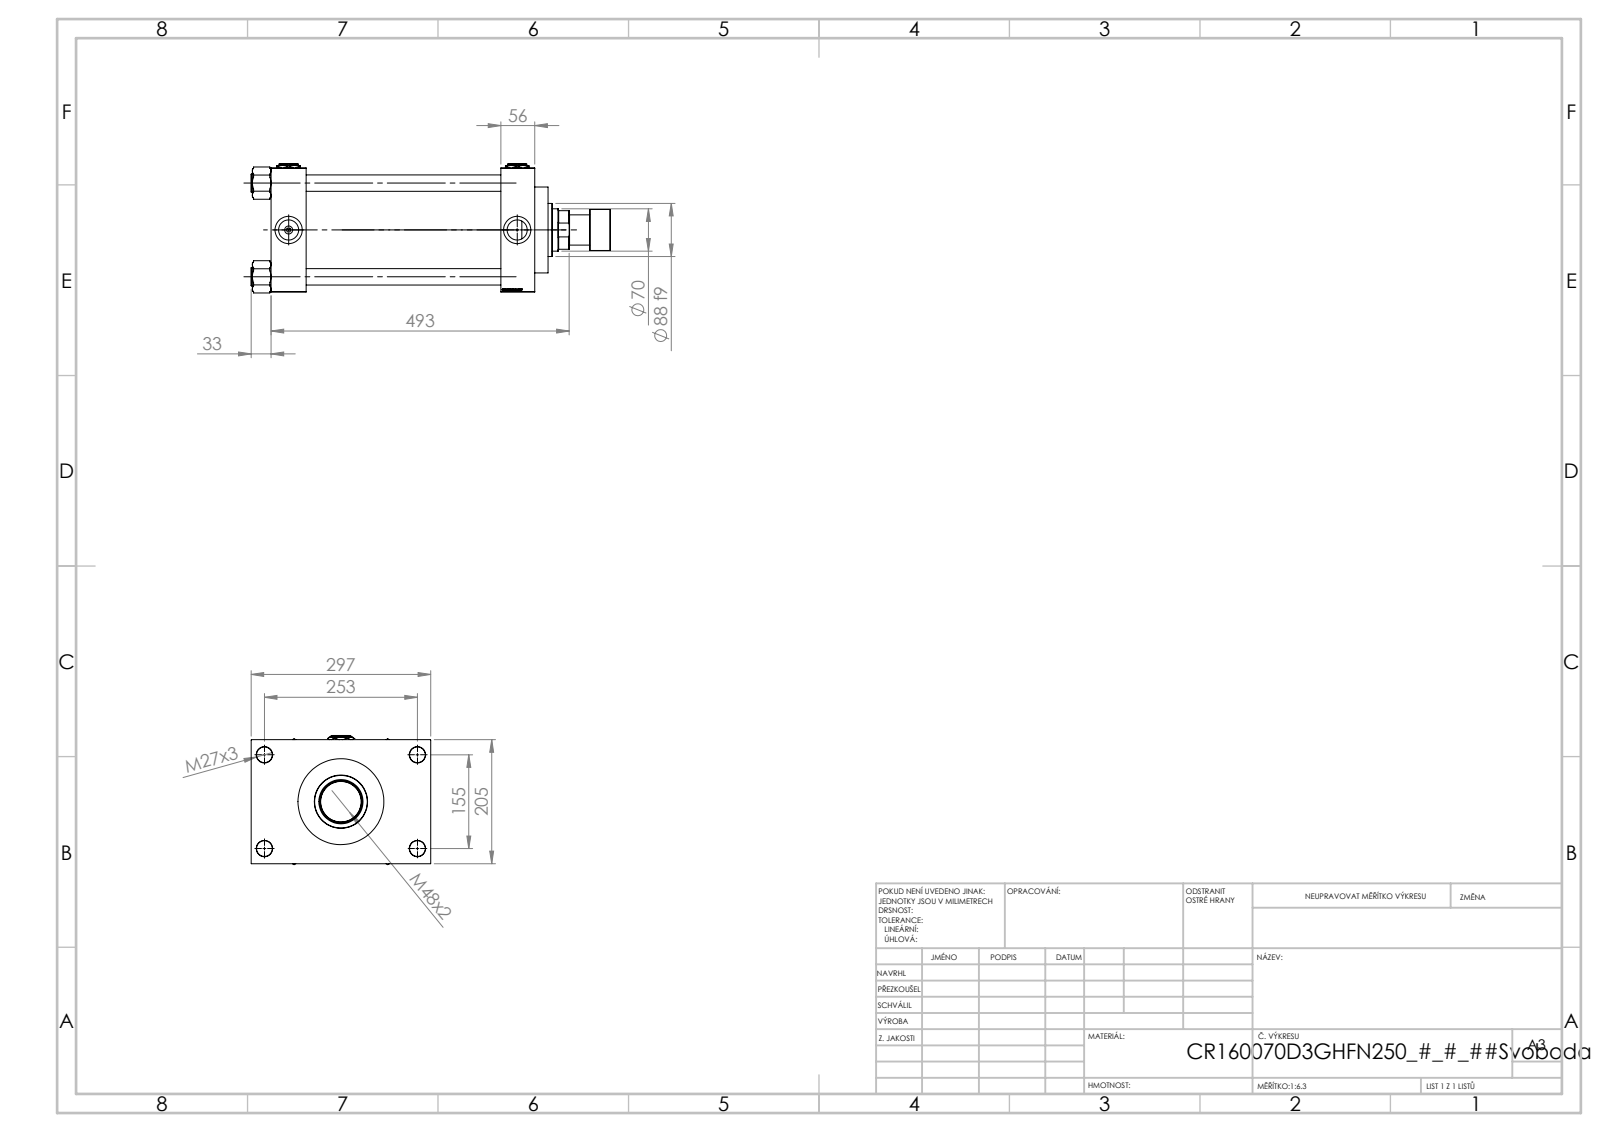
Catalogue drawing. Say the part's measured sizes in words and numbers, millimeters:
The part is named "V215_VC_A; V215CR_D_Body; NUT_M5_D; V215CR_ROD_END_F (+3 more)". Its 3-D file was written by "SolidWorks 2019 (CONFIG_CONTROL_DESIGN)". It is 14 solids with 1263 faces: 596 planar, 103 cylindrical and 564 other. Overall it measures 594 by 297 by 213.57 millimeters. Its volume is 9 778 000 cubic millimeters and its surface area 1 125 000 square millimeters. Round holes: 4 of diameter 26, 4 of diameter 27, 4 of diameter 33.24, 4 of diameter 45, 3 of diameter 7, 1 of diameter 46.5, 1 of diameter 70, 1 of diameter 73, 1 of diameter 120, 1 of diameter 142, 1 of diameter 160. Round bosses or shafts: 4 of diameter 30, 1 of diameter 166, 1 of diameter 88, 1 of diameter 68, 1 of diameter 50, 1 of diameter 49. The main face-to-face distances are 58, 380, 322, 436, 378, 56, 205, 46, 251, 72. The hole center spacings are 49.05, 109.53, 148.35, 154.9, 162.53, 203.95, 256.13, 155.
